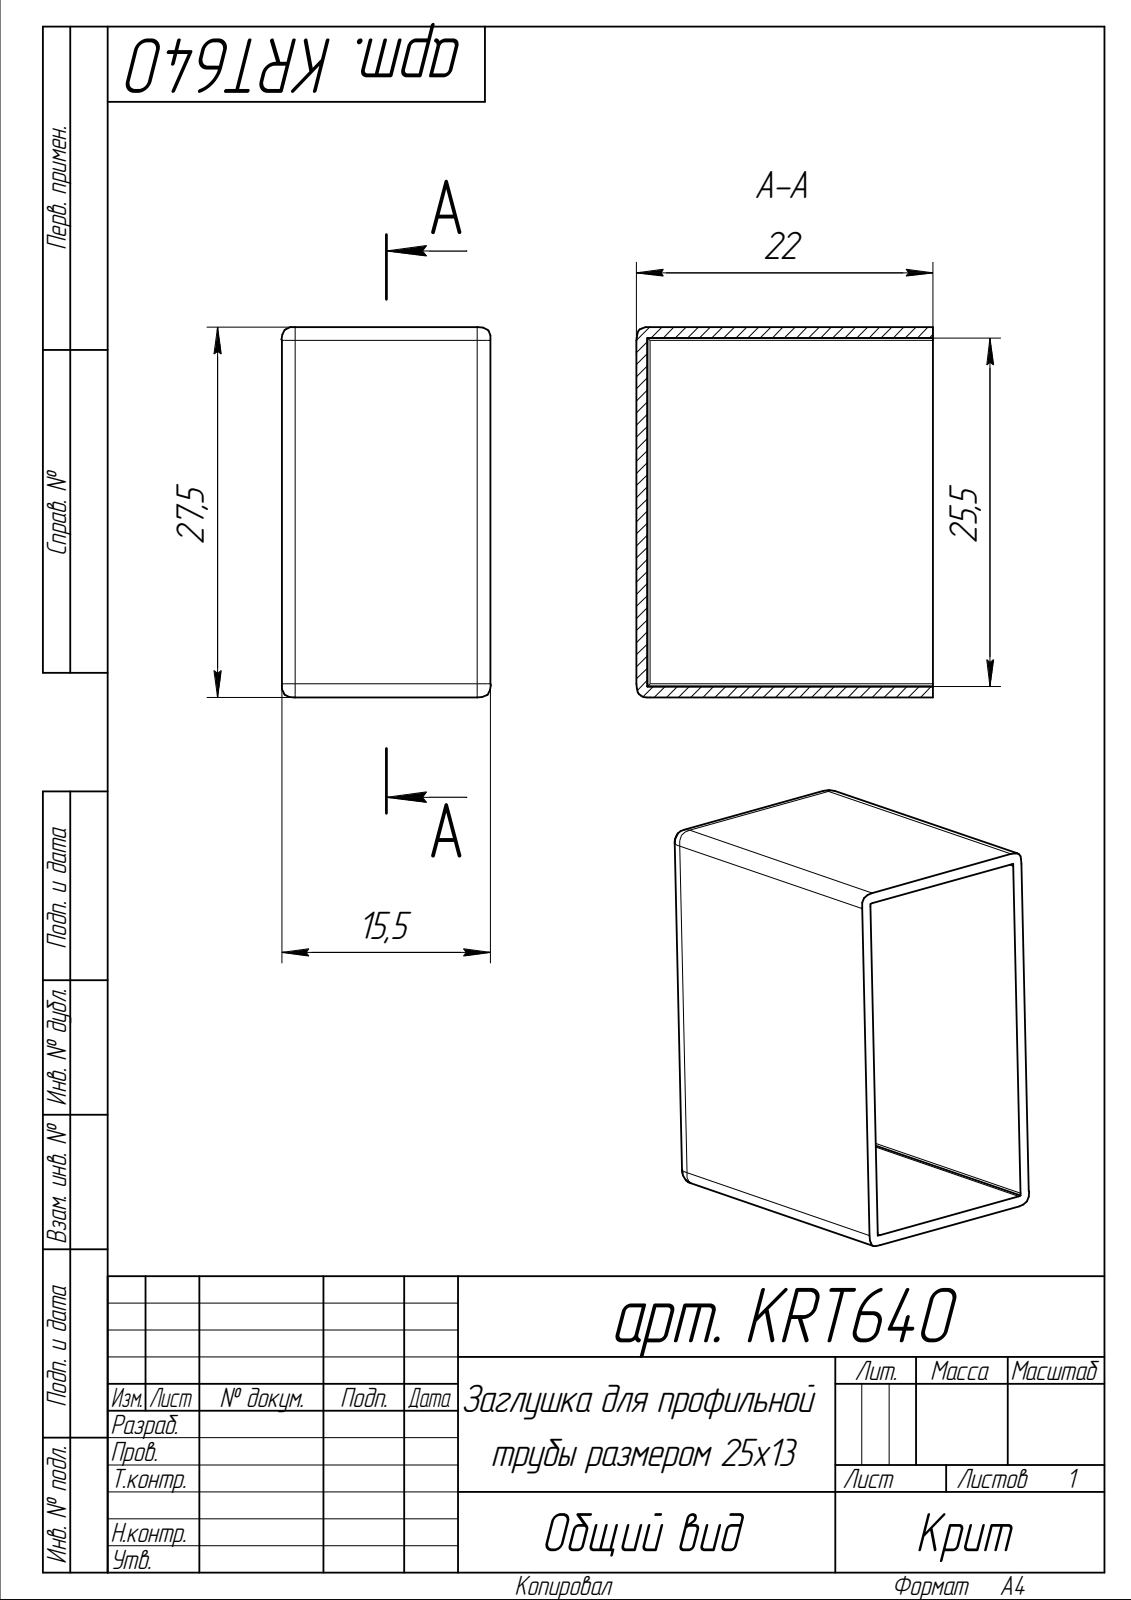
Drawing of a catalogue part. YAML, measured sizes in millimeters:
part_name: "арт. KRT640"
step_written_by: "SolidWorks 2014 (AUTOMOTIVE_DESIGN)"
units: millimeters
bodies: {solids: 1, faces: 47, planar: 11, cylindrical: 0, other: 36}
overall_size: [27.5, 22, 15.5]
volume: 1725
surface_area: 4373
face_to_face_distances: [0.8, 14.7, 26.7, 13.9, 15.5, 27.5, 25.9, 21.2, 22]
